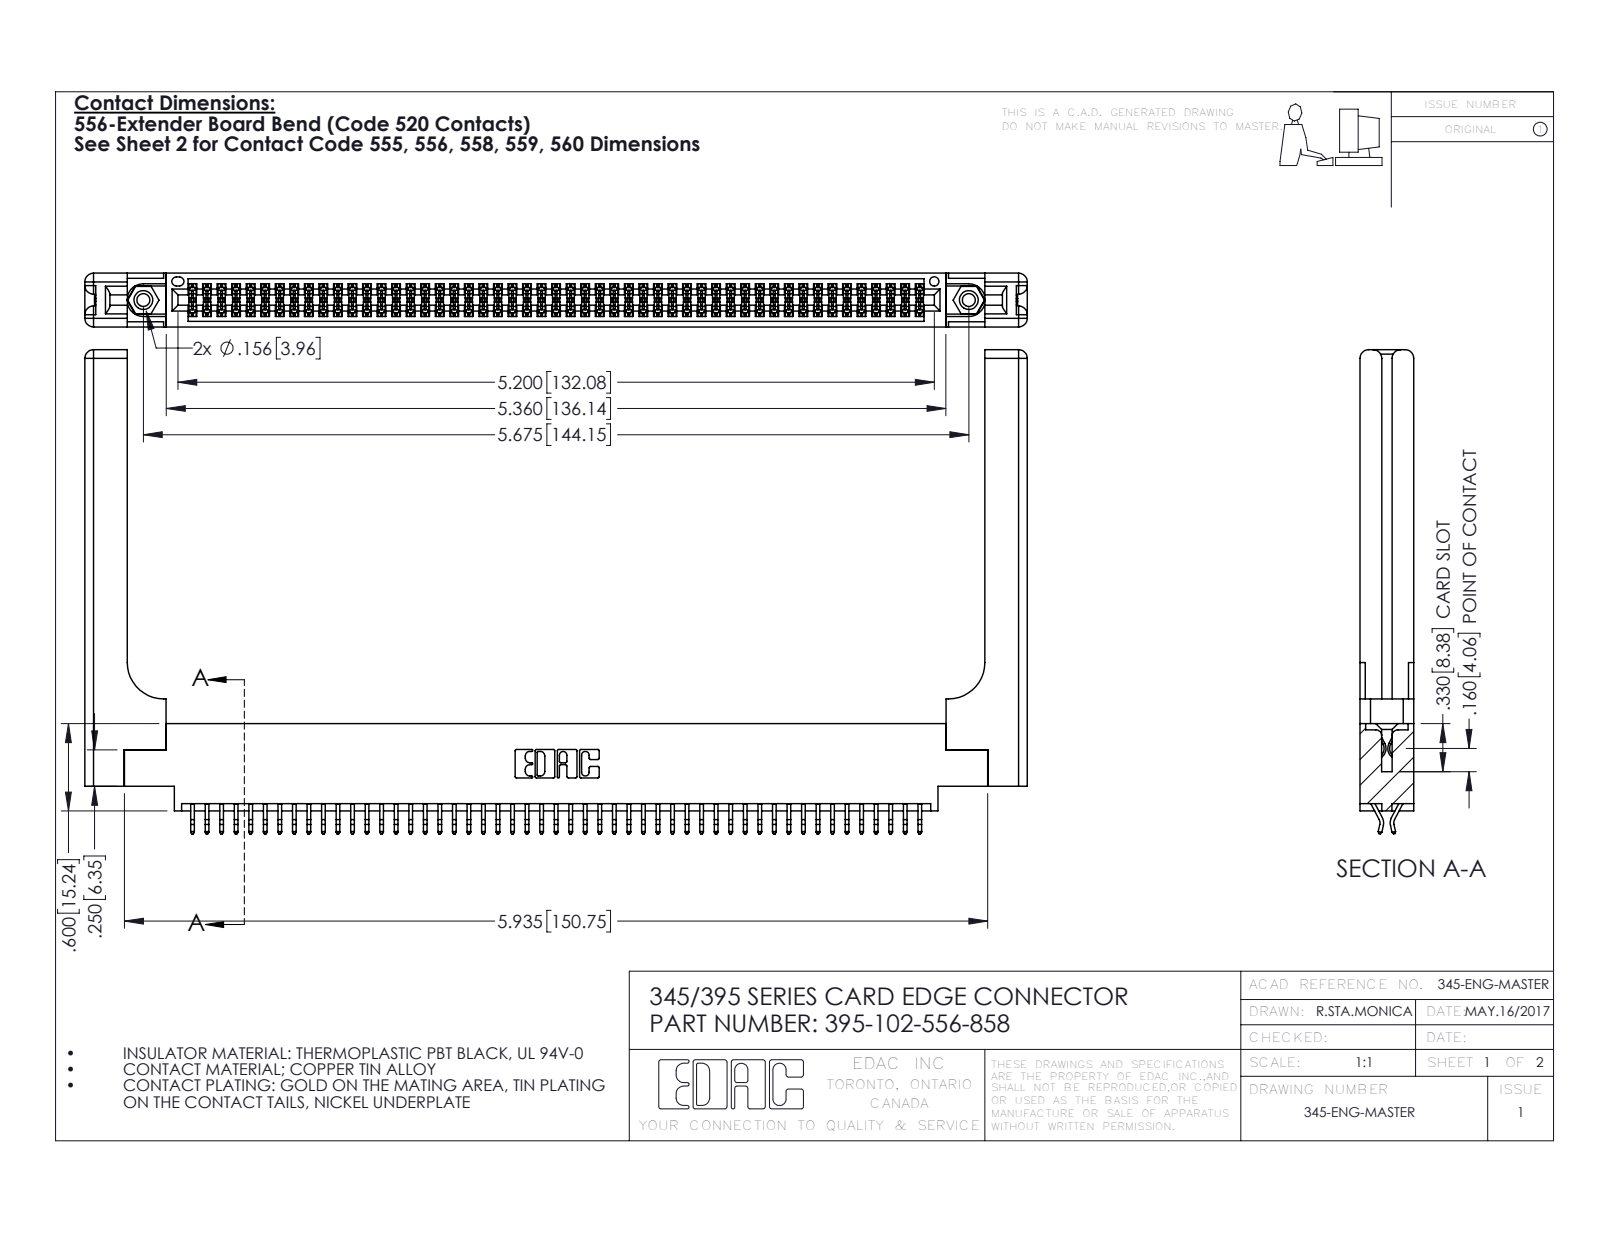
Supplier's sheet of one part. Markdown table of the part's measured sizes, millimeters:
| quantity | value |
| --- | --- |
| part name | 345-292-001_556 Tail; 345-250-001_345-250-001-102; 345-220-058_345-220-058; 345 Part_0.170 Offset - 0.156 Dia-TH (+1 more) |
| STEP written by | SolidWorks 2016 (CONFIG_CONTROL_DESIGN) |
| units | millimeters |
| bodies | 107 solids, 6098 faces (4006 planar, 2032 cylindrical, 60 other) |
| overall size | 164.6 × 84.5 × 9.4 |
| volume | 24 430 mm³ |
| surface area | 28 860 mm² |
| round holes (diameter × count) | 2.3 × 2, 3.2 × 2, 4 × 2, 1.6 × 1 |
| round bosses / shafts (diameter × count) | 3.9 × 2 |
| partial cylindrical surfaces (radius × count) | 0.2 × 153, 0.3 × 22, 1.5 × 16, 0.2 × 6, 0.8 × 6, 0.7 × 3, 0.3 × 2, 0.4 × 2 |
| main face-to-face distances | 1.8, 9.4, 7.6, 0.6, 2.5, 6.9, 5.1, 5.7, 3.8, 3.8 |
| hole center spacings | 6.9, 138.2, 144.1 |
